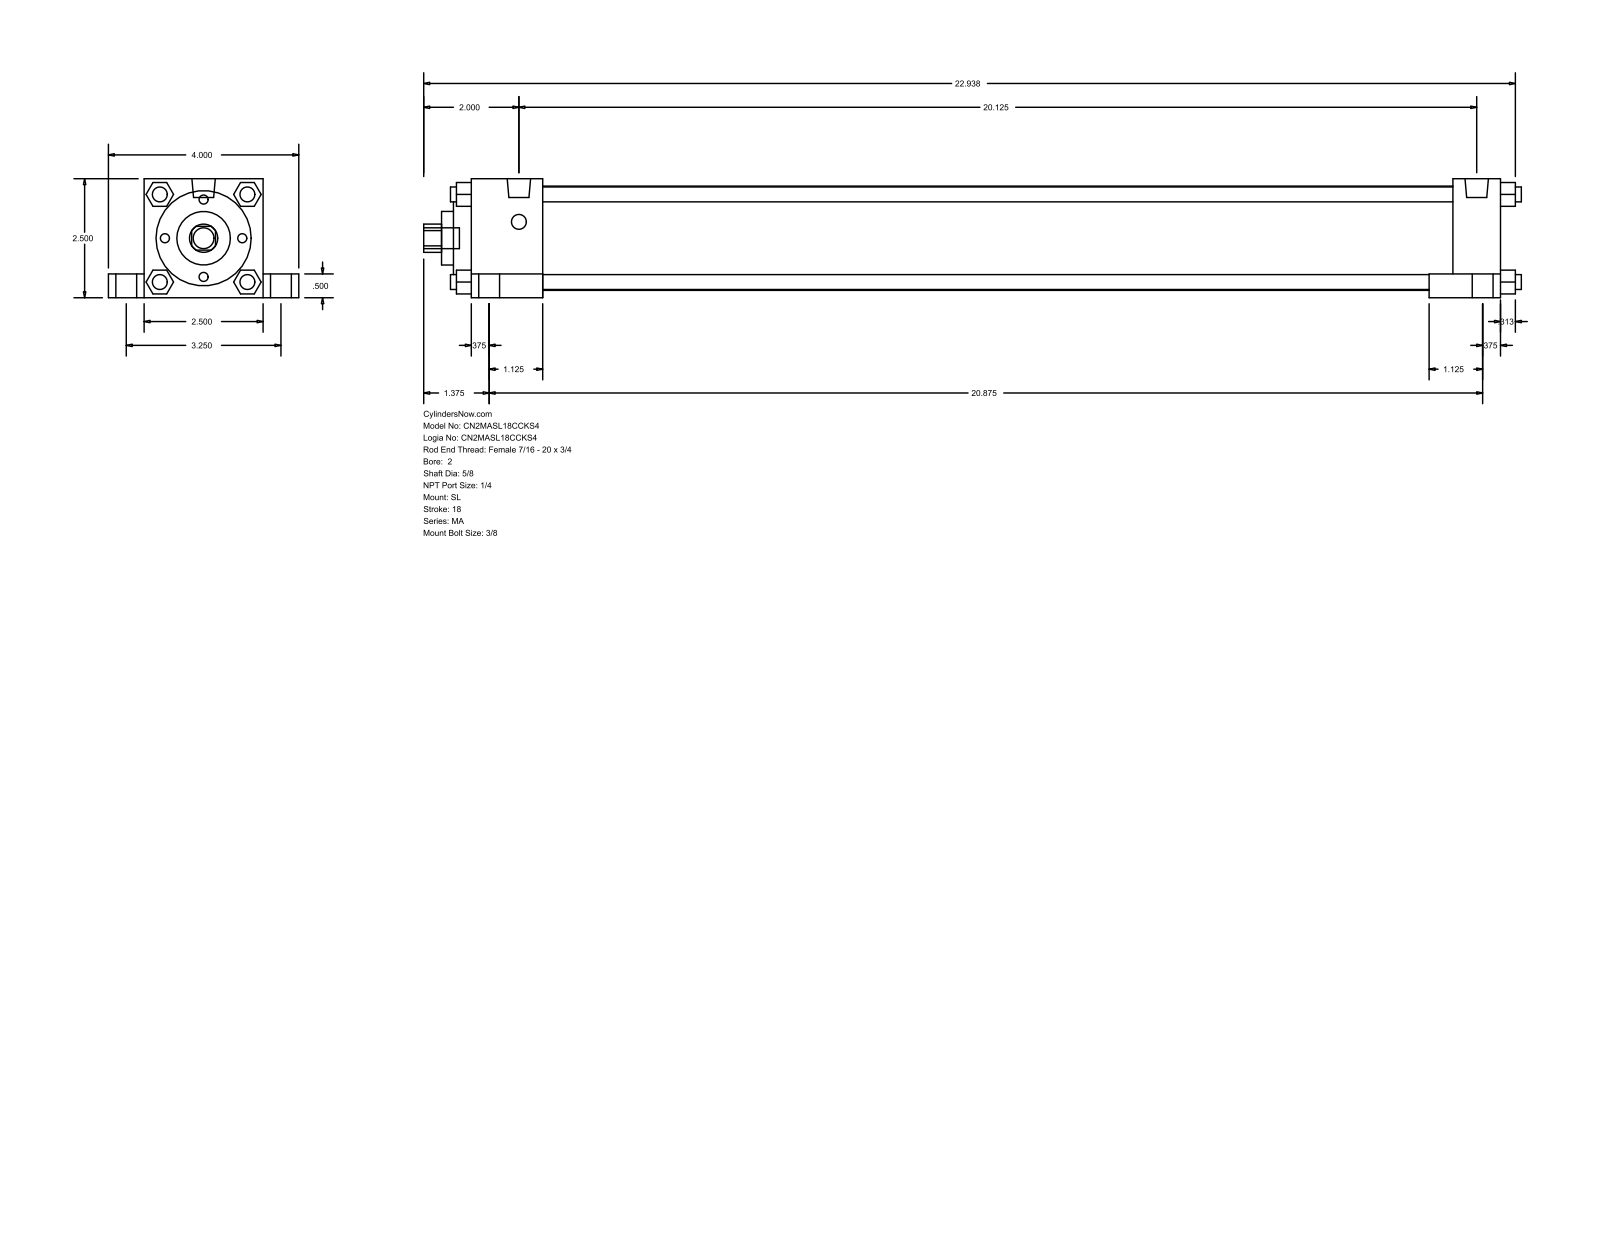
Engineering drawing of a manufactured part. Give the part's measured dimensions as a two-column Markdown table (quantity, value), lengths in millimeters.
| quantity | value |
| --- | --- |
| part name | MA_SL__0200_0.625 |
| STEP written by | GSSL Pune (CONFIG_CONTROL_DESIGN) |
| units | millimeters |
| bodies | 0 solids, 150 faces (113 planar, 37 cylindrical, 0 other) |
| overall size | 585.79 × 101.6 × 63.5 |
| round holes (diameter × count) | 15.88 × 1, 28.57 × 1, 50.8 × 1, 55.63 × 1 |
| round bosses / shafts (diameter × count) | 7.94 × 8, 11.11 × 5, 17.46 × 4, 12.49 × 2 |
| partial cylindrical surfaces (radius × count) | 7.54 × 1 |
| main face-to-face distances | 63.5, 12.7, 9.52, 485.77, 25.4, 19.05, 82.55, 38.1, 549.27, 50.8 |
